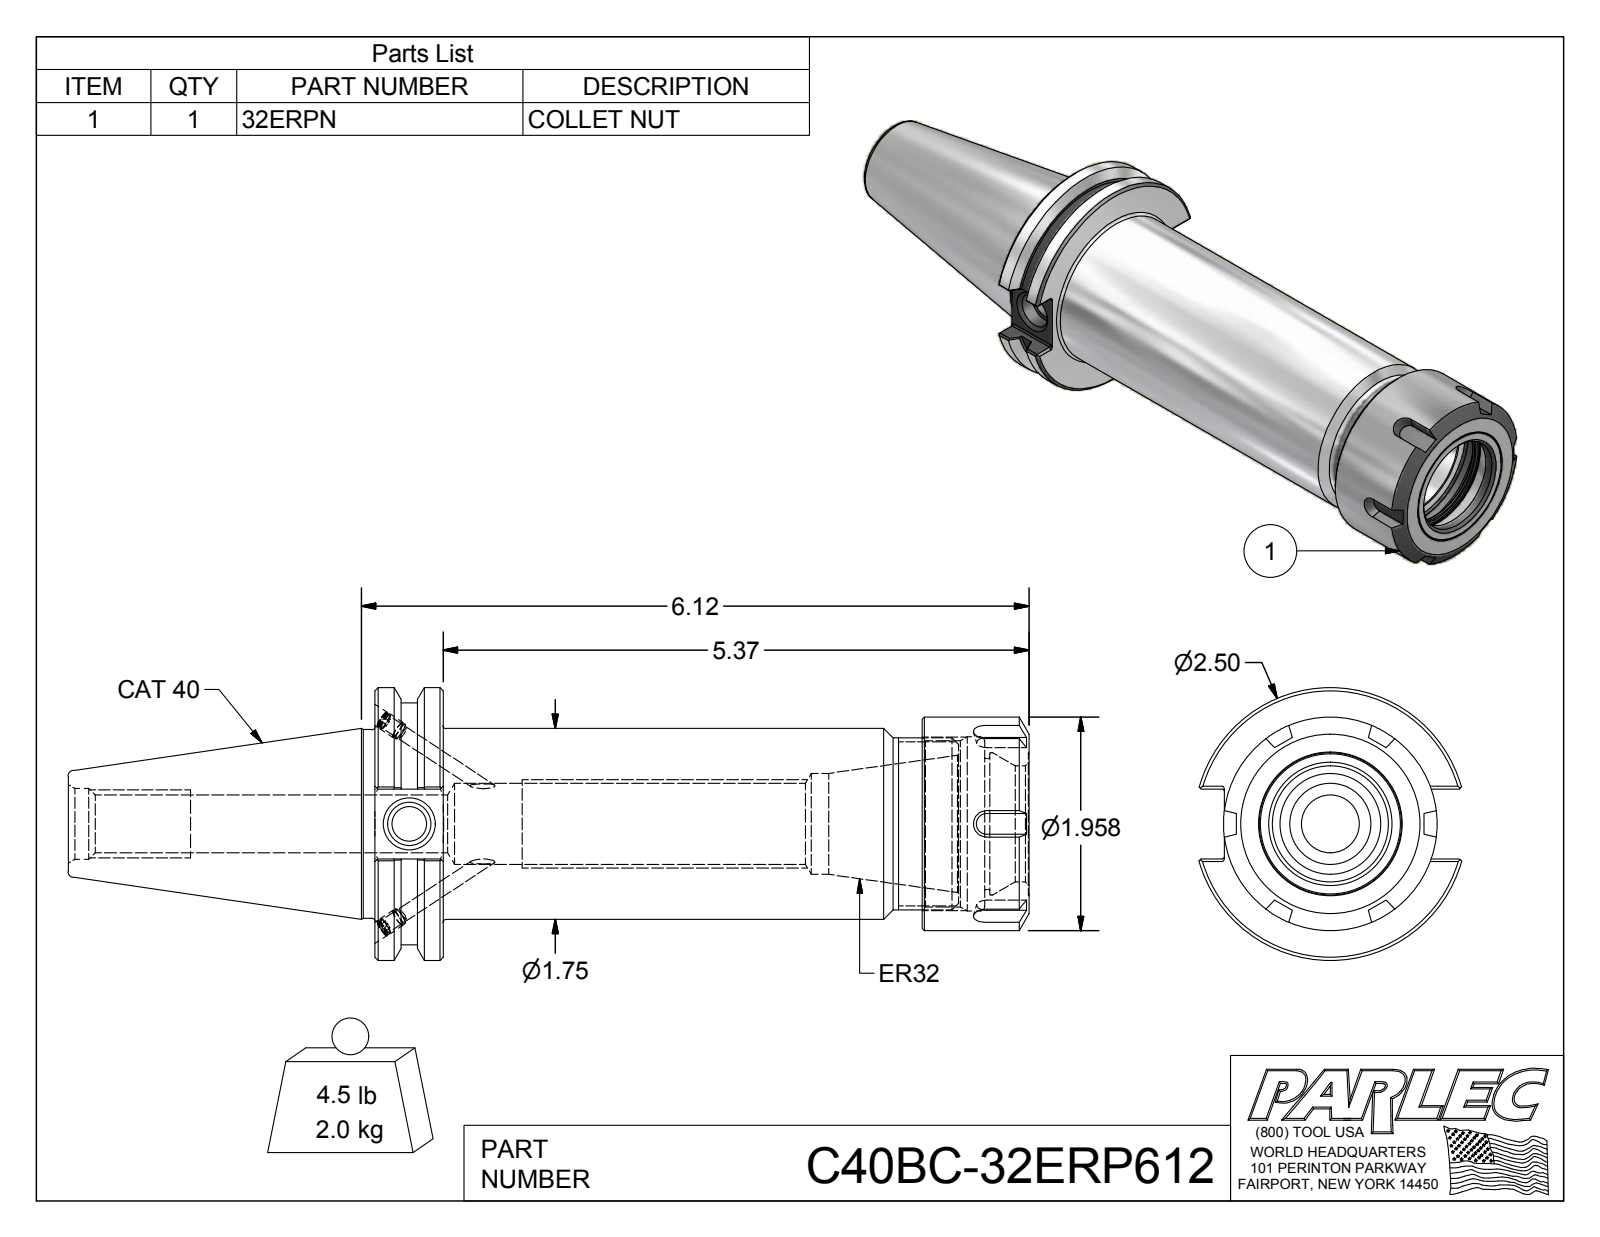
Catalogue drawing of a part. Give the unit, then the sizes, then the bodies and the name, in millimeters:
Units: millimetres
Overall size (bounding box): 223.7 × 63.5 × 61.1
Round holes (diameter × count): ⌀3.3 ×2, ⌀4.1 ×2, ⌀8 ×1, ⌀10.1 ×1, ⌀13.4 ×1, ⌀16.5 ×1, ⌀18.9 ×1, ⌀23.5 ×1, ⌀27 ×1, ⌀30.5 ×1, ⌀33.1 ×1, ⌀38.7 ×1
Round bosses / shafts (diameter × count): ⌀4.2 ×2, ⌀4 ×2, ⌀63.5 ×1, ⌀56.4 ×1, ⌀49.7 ×1, ⌀44.5 ×1, ⌀43.9 ×1, ⌀40 ×1
Partial cylindrical surfaces — rounded edges, fillets, slot ends (radius × count): R0.5 ×12
Main face-to-face distances: 15.9, 152.3, 136.4, 127.4, 111.6, 24.8, 141.9, 126.1, 14.5, 10.3
Volume: 258 900 mm³ · Surface area: 54 080 mm²
Bodies: 4 solids, 175 faces (76 planar, 43 cylindrical, 56 other)
Part name (STEP PRODUCT): C40BC-32ERP612; C40BCB-32ER6-1; 029-965; 32ERPN
STEP written by: Autodesk Inventor 2012 (AUTOMOTIVE_DESIGN)
